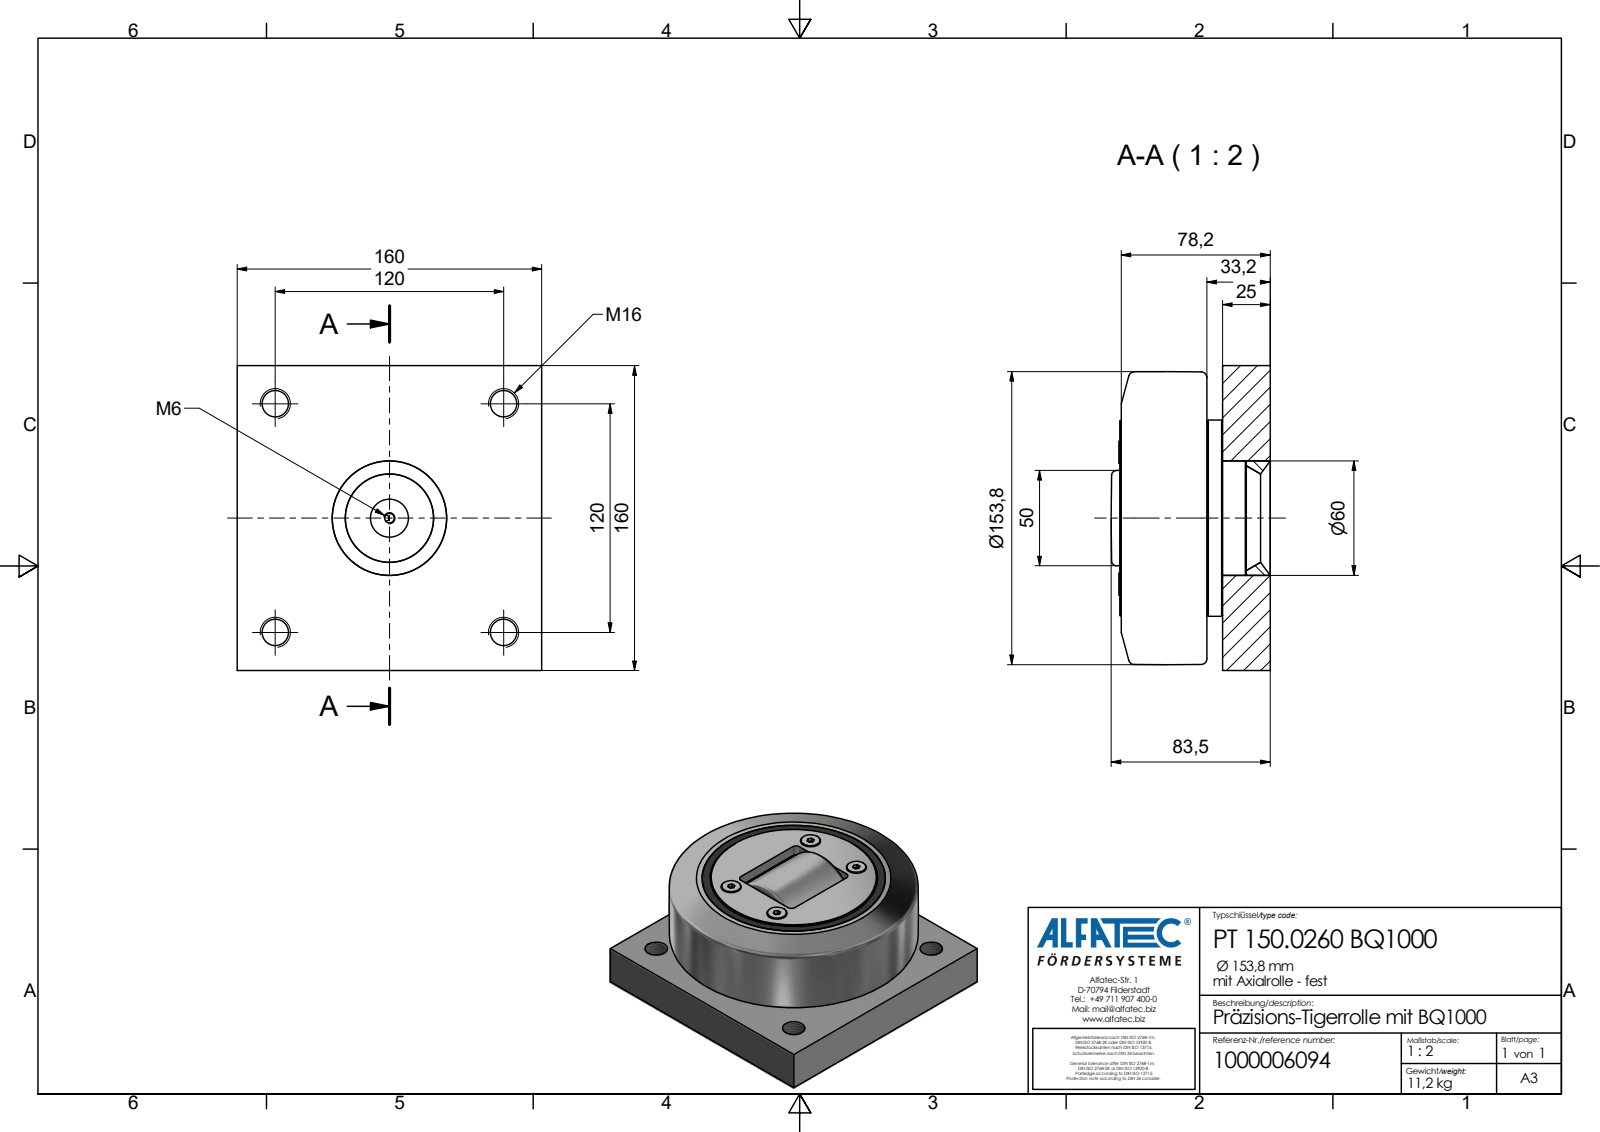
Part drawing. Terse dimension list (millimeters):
name: PT 150.0260 BQ1000_Kontur
written by: Autodesk Inventor 2020 (AP242_MANAGED_MODEL_BASED_3D_ENGINEERING_MIM_LF)
unit: mm
bodies: 1 solid, 69 faces (44 planar, 11 cylindrical, 14 other)
size: 160 × 160 × 83.5
volume: 1 521 000 mm³; area: 113 512 mm²
holes: 4× ⌀13.84
bosses: 4× ⌀11.7, 1× ⌀103, 1× ⌀102.5, 1× ⌀101.4
face distances: 25, 33.2, 8.2, 160, 79, 54, 45.8, 78.2, 53.2, 45
hole spacings: 120, 169.71
